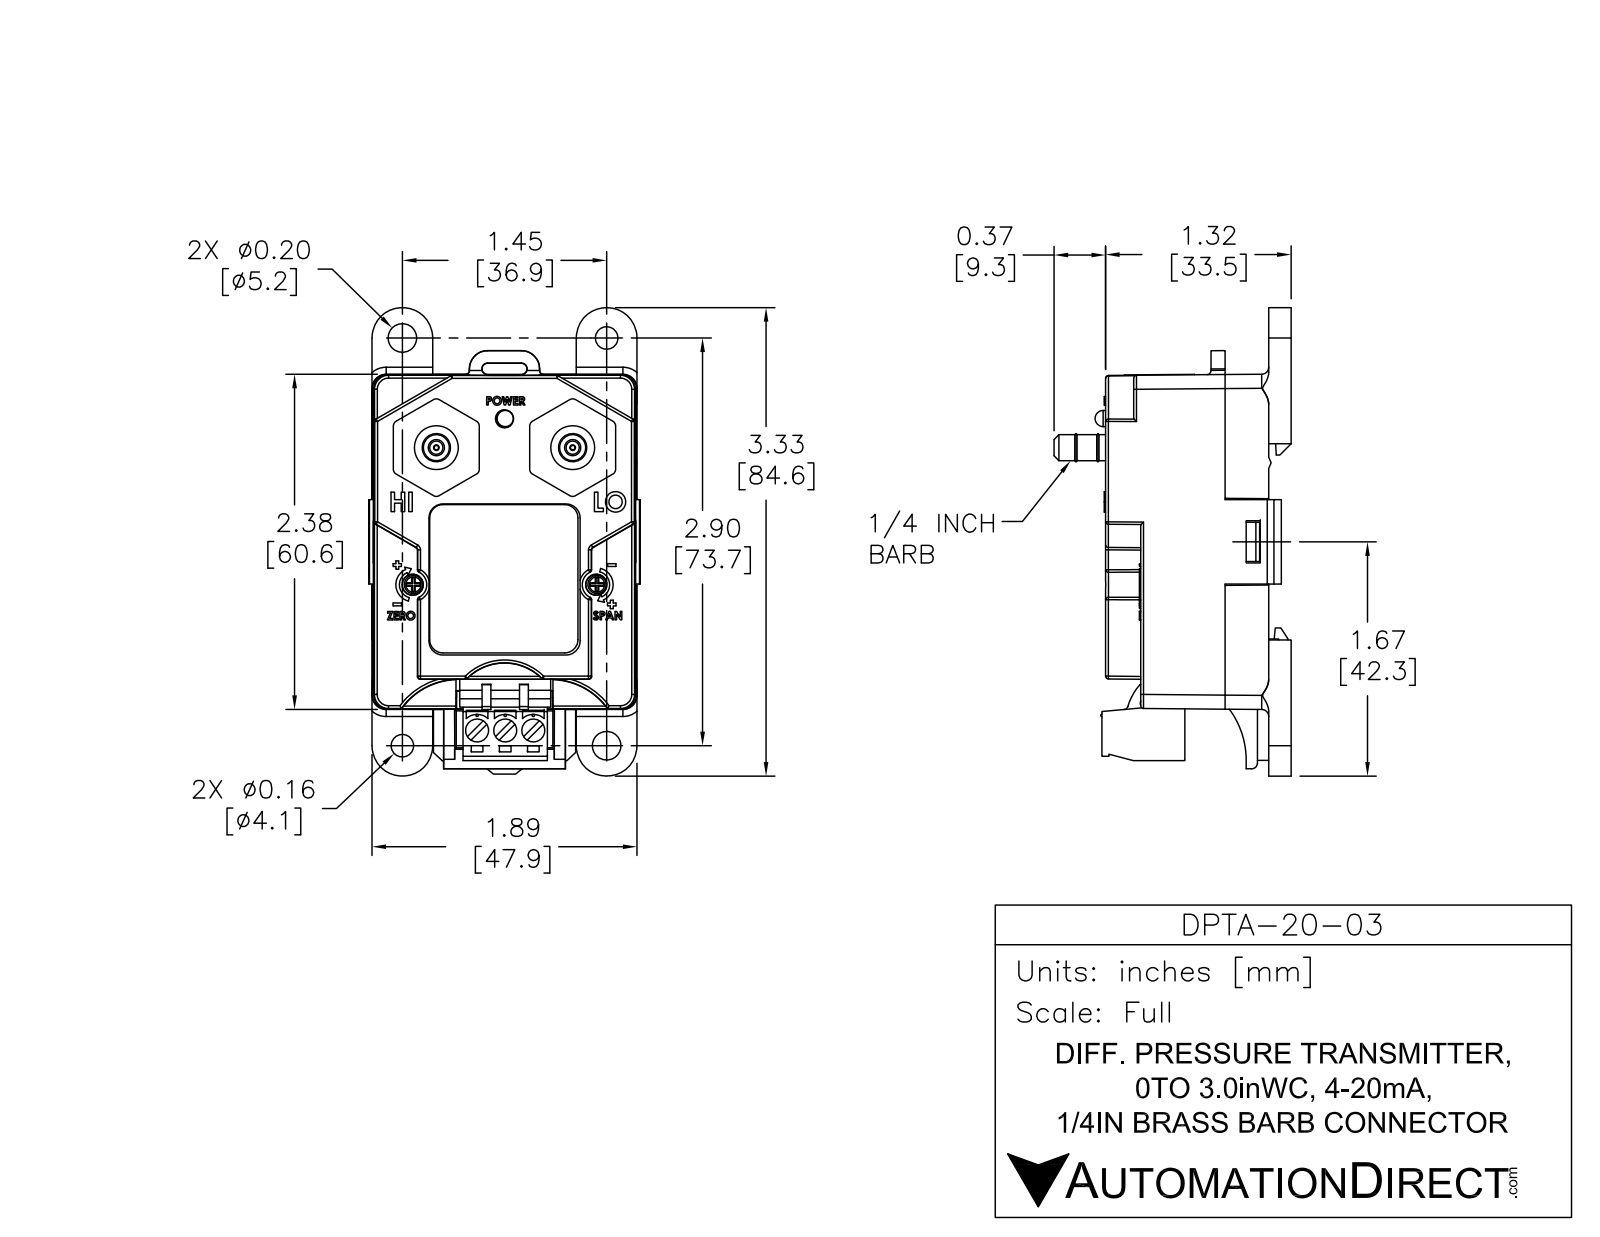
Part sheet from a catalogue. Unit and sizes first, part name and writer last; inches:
Units: inches
Overall size (bounding box): 3.347 × 1.959 × 1.697
Round holes (diameter × count): ⌀0.157 ×7, ⌀0.098 ×2, ⌀0.202 ×2, ⌀0.122 ×1
Round bosses / shafts (diameter × count): ⌀0.197 ×3, ⌀0.138 ×3, ⌀0.138 ×3, ⌀0.315 ×2, ⌀0.187 ×2, ⌀0.118 ×1
Partial cylindrical surfaces — rounded edges, fillets, slot ends (radius × count): R0.118 ×12, R0.079 ×4, R0.217 ×4, R0.039 ×2, R0.042 ×2, R0.044 ×2, R0.094 ×2, R0.128 ×2
Main face-to-face distances: 0.039, 0.075, 0.157, 1.146, 0.02, 1.846, 0.232, 0.197, 1.303, 1.071
Hole centre spacings: 0.533, 0.816, 0.92, 0.981, 1.159, 1.357, 1.444, 1.505
Volume: 1.811 in³ · Surface area: 53.85 in²
Bodies: 11 solids, 506 faces (354 planar, 134 cylindrical, 18 other)
Part name (STEP PRODUCT): DPTA-20-03
STEP written by: SolidWorks 2013 (AUTOMOTIVE_DESIGN)
